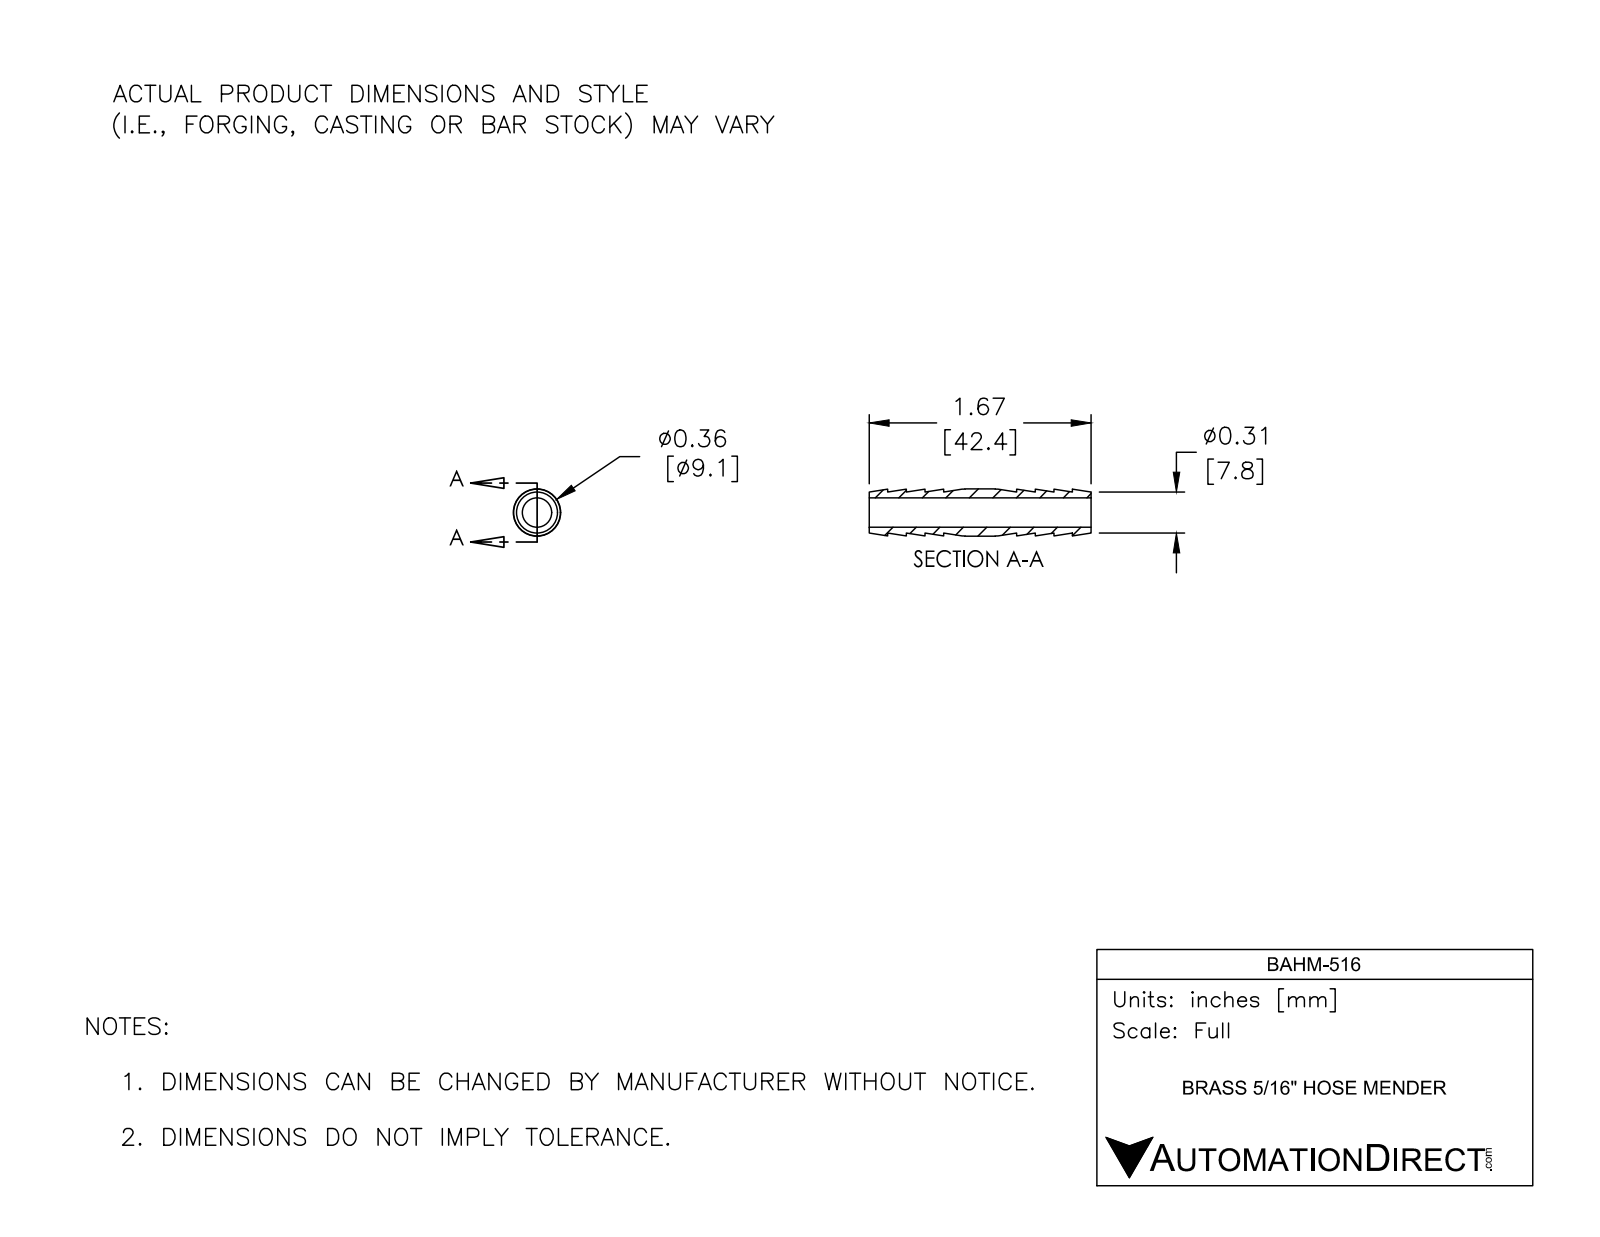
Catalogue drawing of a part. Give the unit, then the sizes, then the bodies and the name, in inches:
Units: inches
Overall size (bounding box): 1.67 × 0.357 × 0.357
Round holes (diameter × count): ⌀0.222 ×1
Round bosses / shafts (diameter × count): ⌀0.357 ×1, ⌀0.353 ×1
Main face-to-face distances: 0.14, 0.28, 0.42, 1.11, 1.25, 0.83, 0.56, 1.39, 1.53, 0.14
Volume: 0.083 in³ · Surface area: 3.202 in²
Bodies: 1 solid, 40 faces (12 planar, 8 cylindrical, 20 other)
Part name (STEP PRODUCT): BAHM-516
STEP written by: SolidWorks 2017 (AUTOMOTIVE_DESIGN)
